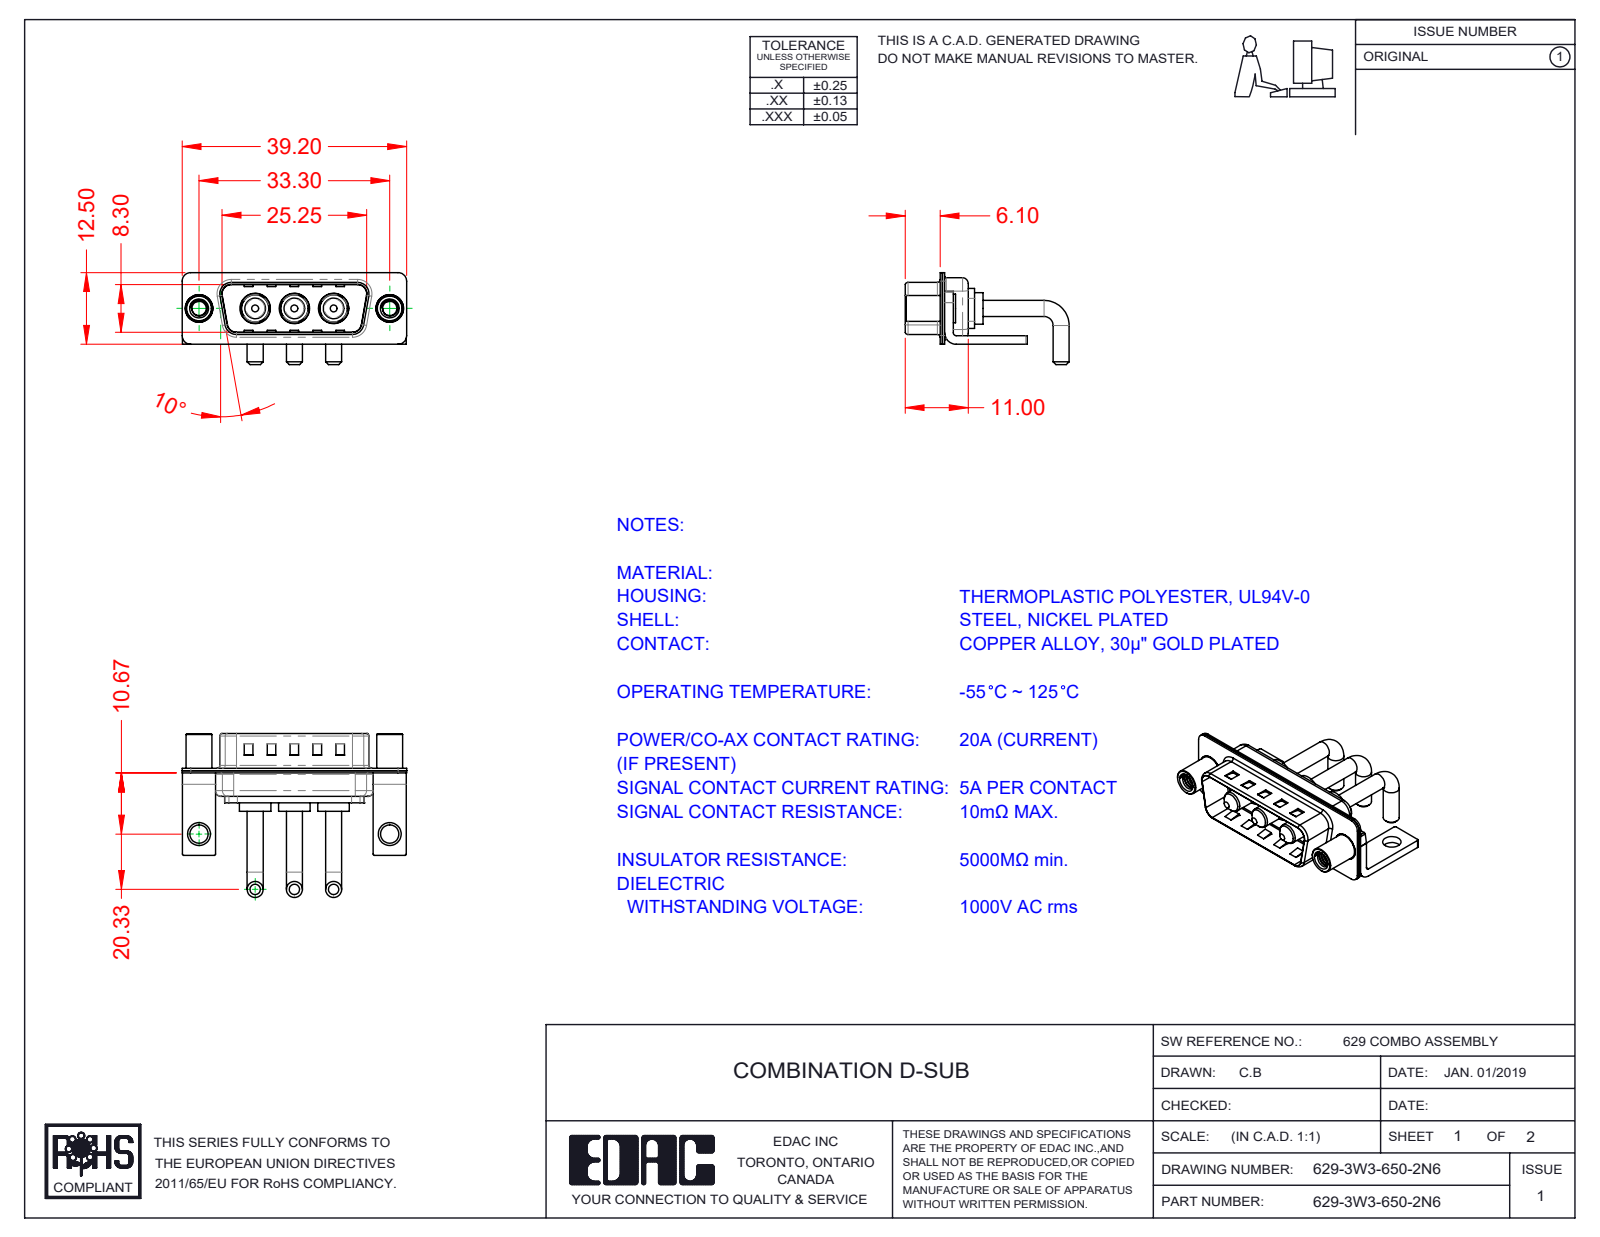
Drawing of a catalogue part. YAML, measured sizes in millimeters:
part_name: "629Combo Stabilizer Bracket; 629Combo Shell Rear_15 Contacts; 629-3W3-650-2N6; Power Pin_Ext 20A RA (+3 more)"
step_written_by: "SolidWorks 2020 (CONFIG_CONTROL_DESIGN)"
units: millimeters
bodies: {solids: 13, faces: 567, planar: 191, cylindrical: 268, other: 108}
overall_size: [39.2, 28.63, 16.05]
volume: 2767
surface_area: 6102
round_holes:
  - {diameter: 4.85, count: 3}
  - {diameter: 5.3, count: 3}
  - {diameter: 2.5, count: 2}
  - {diameter: 3.2, count: 2}
  - {diameter: 4, count: 2}
  - {diameter: 4.8, count: 2}
round_bosses_or_shafts:
  - {diameter: 2.8, count: 6}
  - {diameter: 5.5, count: 3}
  - {diameter: 5.2, count: 3}
  - {diameter: 4.75, count: 3}
  - {diameter: 3.75, count: 3}
  - {diameter: 3.6, count: 3}
  - {diameter: 5, count: 2}
  - {diameter: 4.9, count: 2}
partial_cylinders:
  - {radius: 0.25, count: 16}
  - {radius: 1.5, count: 16}
  - {radius: 2, count: 13}
  - {radius: 0.5, count: 9}
  - {radius: 1.6, count: 8}
  - {radius: 0.6, count: 4}
  - {radius: 0.65, count: 4}
  - {radius: 0.9, count: 4}
face_to_face_distances: [0.4, 0.8, 1.5, 9.5, 9.1, 8.7, 9.9, 5.2, 0.75, 0.6]
hole_center_spacings: [6.85, 9.8, 16.65, 23.5, 33.3, 13.7]
